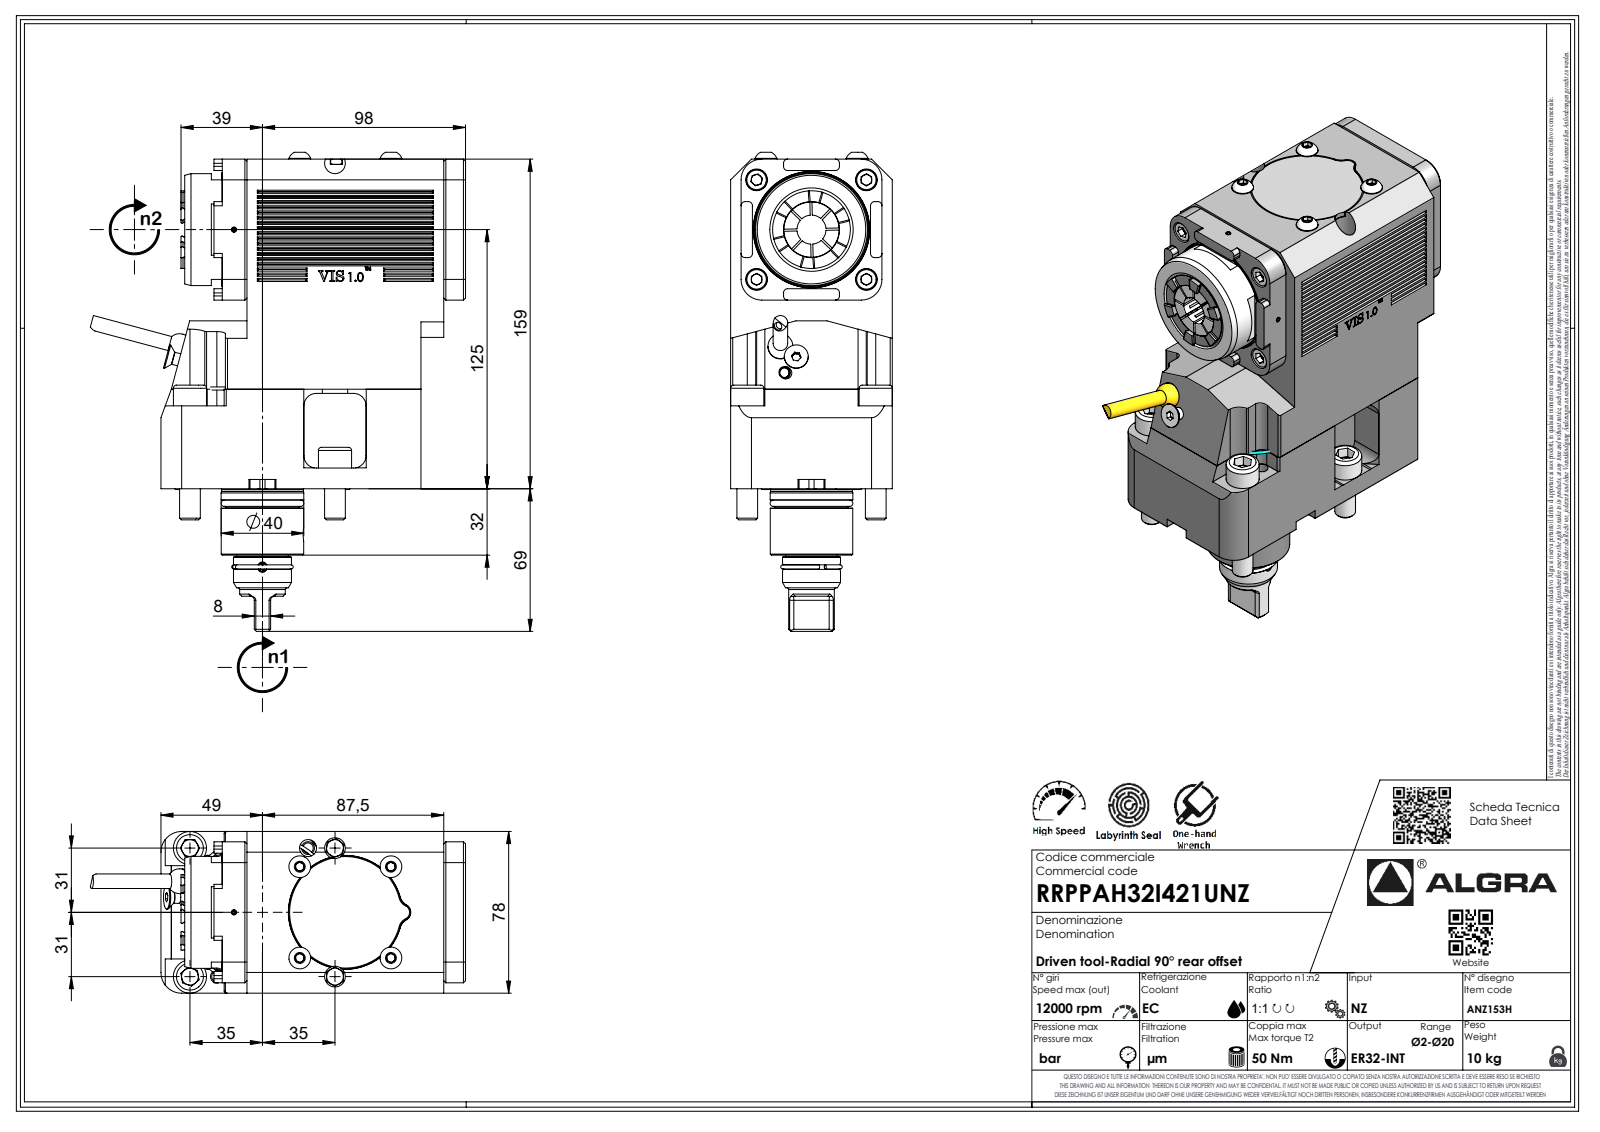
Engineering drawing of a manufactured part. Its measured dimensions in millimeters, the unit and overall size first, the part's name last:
Units: millimetres
Overall size (bounding box): 231.1 × 181.57 × 78
Round holes (diameter × count): ⌀2.1 ×1, ⌀4 ×1
Round bosses / shafts (diameter × count): ⌀16 ×4, ⌀10.5 ×4, ⌀10 ×4, ⌀54 ×1, ⌀39.9 ×1, ⌀39.8 ×1, ⌀39.5 ×1, ⌀35.1 ×1
Partial cylindrical surfaces — rounded edges, fillets, slot ends (radius × count): R2 ×23, R5 ×16, R1 ×8, R0.33 ×7, R0.52 ×7, R3.7 ×7, R10 ×6, R6 ×4
Main face-to-face distances: 78, 159, 22, 11, 11.5, 56.5, 30, 73, 16.5, 61.5
Volume: 1 481 000 mm³ · Surface area: 105 246 mm²
Bodies: 1 solid, 624 faces (390 planar, 124 cylindrical, 110 other)
Part name (STEP PRODUCT): RRPPAH32I421UNZ
STEP written by: SolidWorks 2023 (AUTOMOTIVE_DESIGN)
